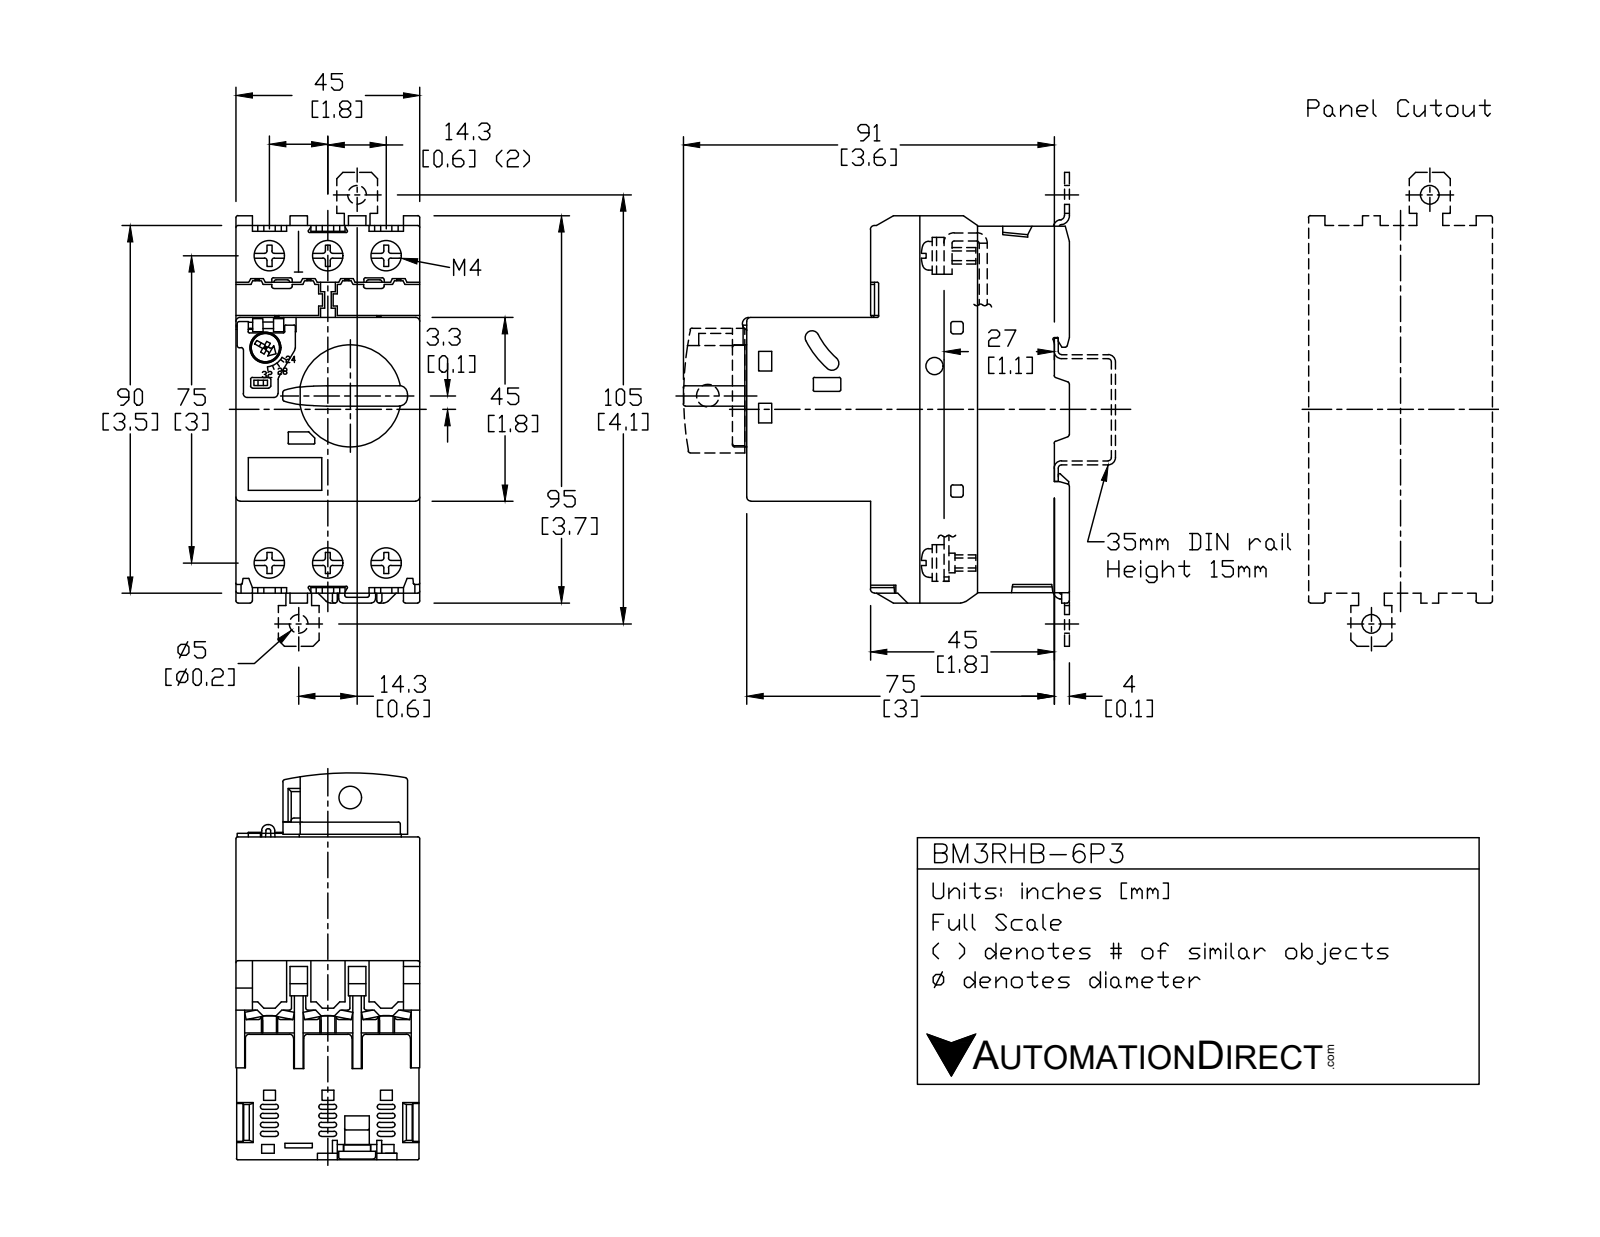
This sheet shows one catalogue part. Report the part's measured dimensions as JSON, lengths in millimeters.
{"part_name": "BM3RHB-6P3", "step_written_by": "SolidWorks 2018 (AUTOMOTIVE_DESIGN)", "units": "millimeters", "bodies": {"solids": 25, "faces": 1294, "planar": 964, "cylindrical": 327, "other": 3}, "overall_size": [94.8, 94.5, 45], "volume_mm3": 231500, "surface_area_mm2": 57040, "round_holes": [[4, 6], [7.4, 6], [1.6, 1], [4.2, 1], [5, 1], [5.5, 1], [7.5, 1]], "round_bosses_or_shafts": [[6, 6], [25, 1], [7, 1]], "partial_cylinders_radius": [[0.5, 67], [0.6, 24], [2, 14], [0.3, 12], [1, 8], [2.5, 8], [0.2, 6], [1.5, 2]], "face_to_face_distances": [45, 36.6, 42.4, 79, 22.4, 67.4, 3, 16.5, 20.1, 12], "hole_center_spacings": [14.3, 76.4, 75, 28.6, 80.3, 22.4, 23.9, 27.1]}
